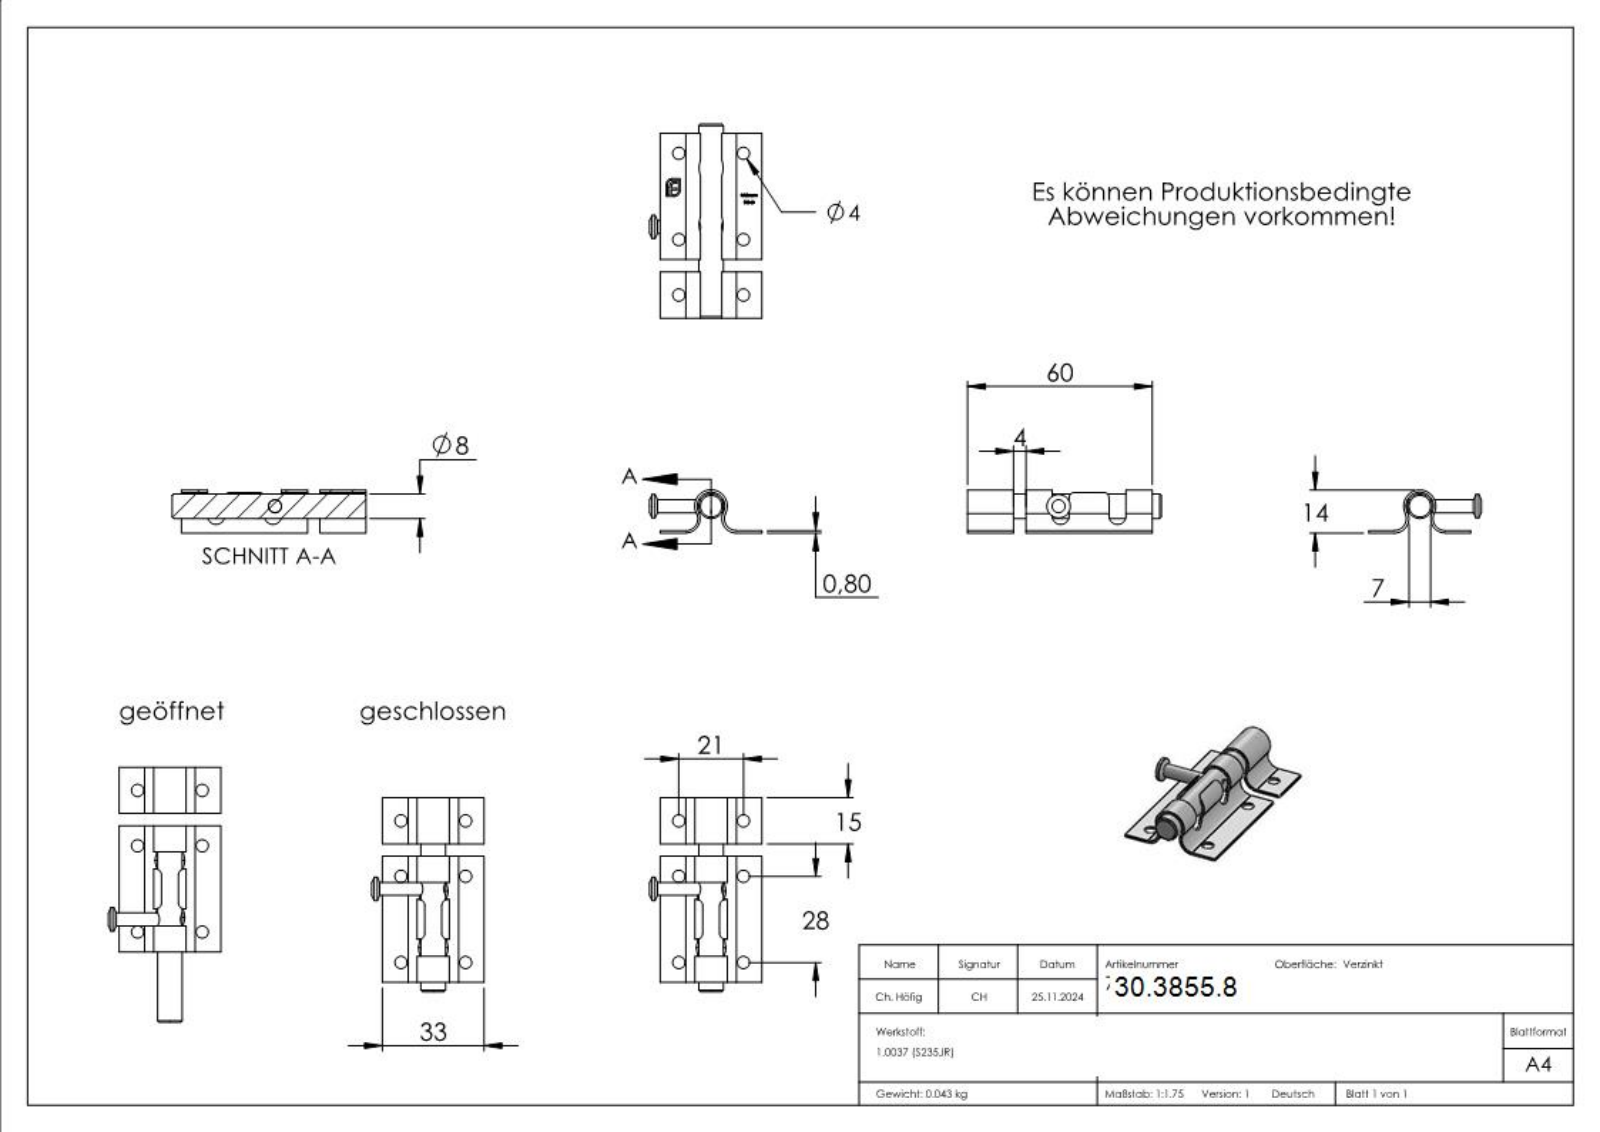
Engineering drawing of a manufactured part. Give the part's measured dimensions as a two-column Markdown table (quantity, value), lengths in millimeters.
| quantity | value |
| --- | --- |
| part name | 700-XXX Teil2_700-60 Teil2; 700-XXX Teil3_700-XXX Teil3; 700-60; 700-XXX Teil1_700-60 Teil1 |
| STEP written by | SolidWorks 2018 (CONFIG_CONTROL_DESIGN) |
| units | millimeters |
| bodies | 4 solids, 285 faces (137 planar, 40 cylindrical, 108 other) |
| overall size | 63 × 36.5 × 14 |
| volume | 5 490 mm³ |
| surface area | 7 712 mm² |
| round holes (diameter × count) | 4 × 6, 4.2 × 1 |
| round bosses / shafts (diameter × count) | 8 × 1, 7.6 × 1 |
| partial cylindrical surfaces (radius × count) | 2 × 4, 2.75 × 2, 3.89 × 2, 4.69 × 2, 4.45 × 1, 5.25 × 1 |
| main face-to-face distances | 0.8, 33, 15, 60, 45, 19, 4, 41, 63, 48 |
| hole center spacings | 21, 18, 27.66, 28, 35, 46, 50.57 |
